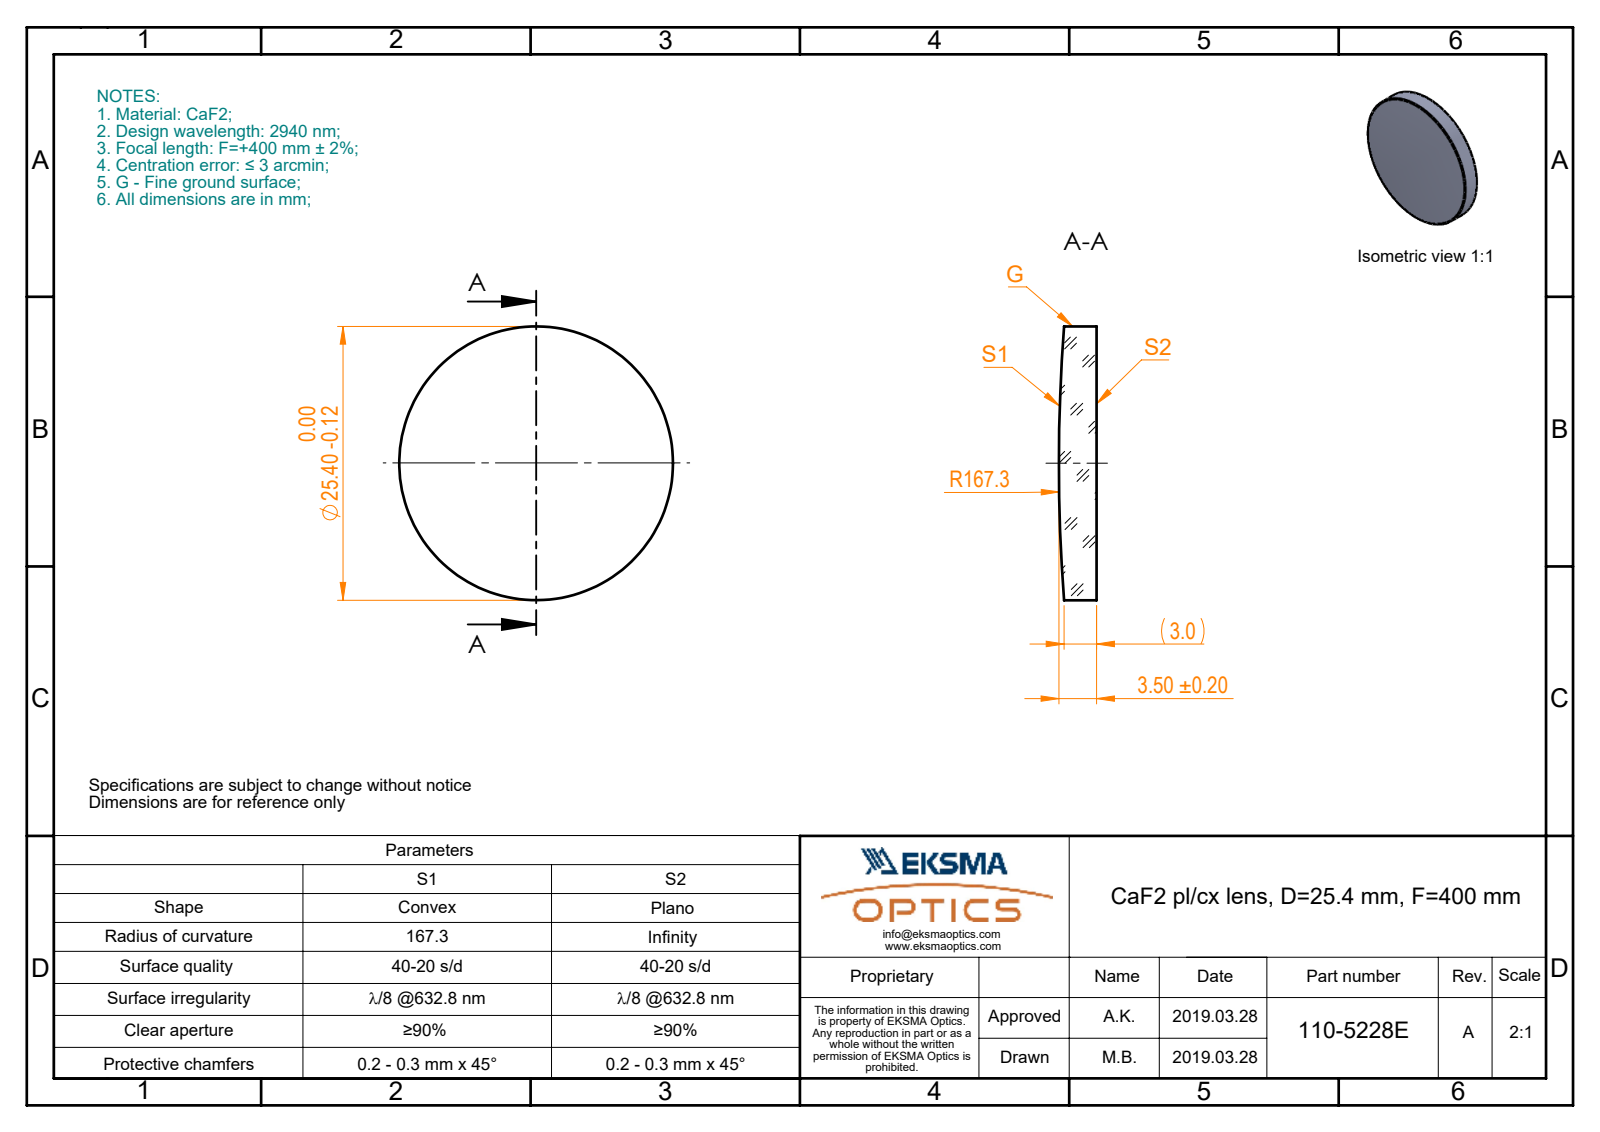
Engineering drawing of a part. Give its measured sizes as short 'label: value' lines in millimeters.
name: 110-5228E CaF2 pl-cx 25.4 F400
written by: SolidWorks 2017 (CONFIG_CONTROL_DESIGN)
unit: mm
bodies: 1 solid, 5 faces (1 planar, 2 cylindrical, 2 other)
size: 25.4 × 25.4 × 3.5
volume: 1 651 mm³; area: 1 255 mm²
bosses: 1× ⌀25.4
